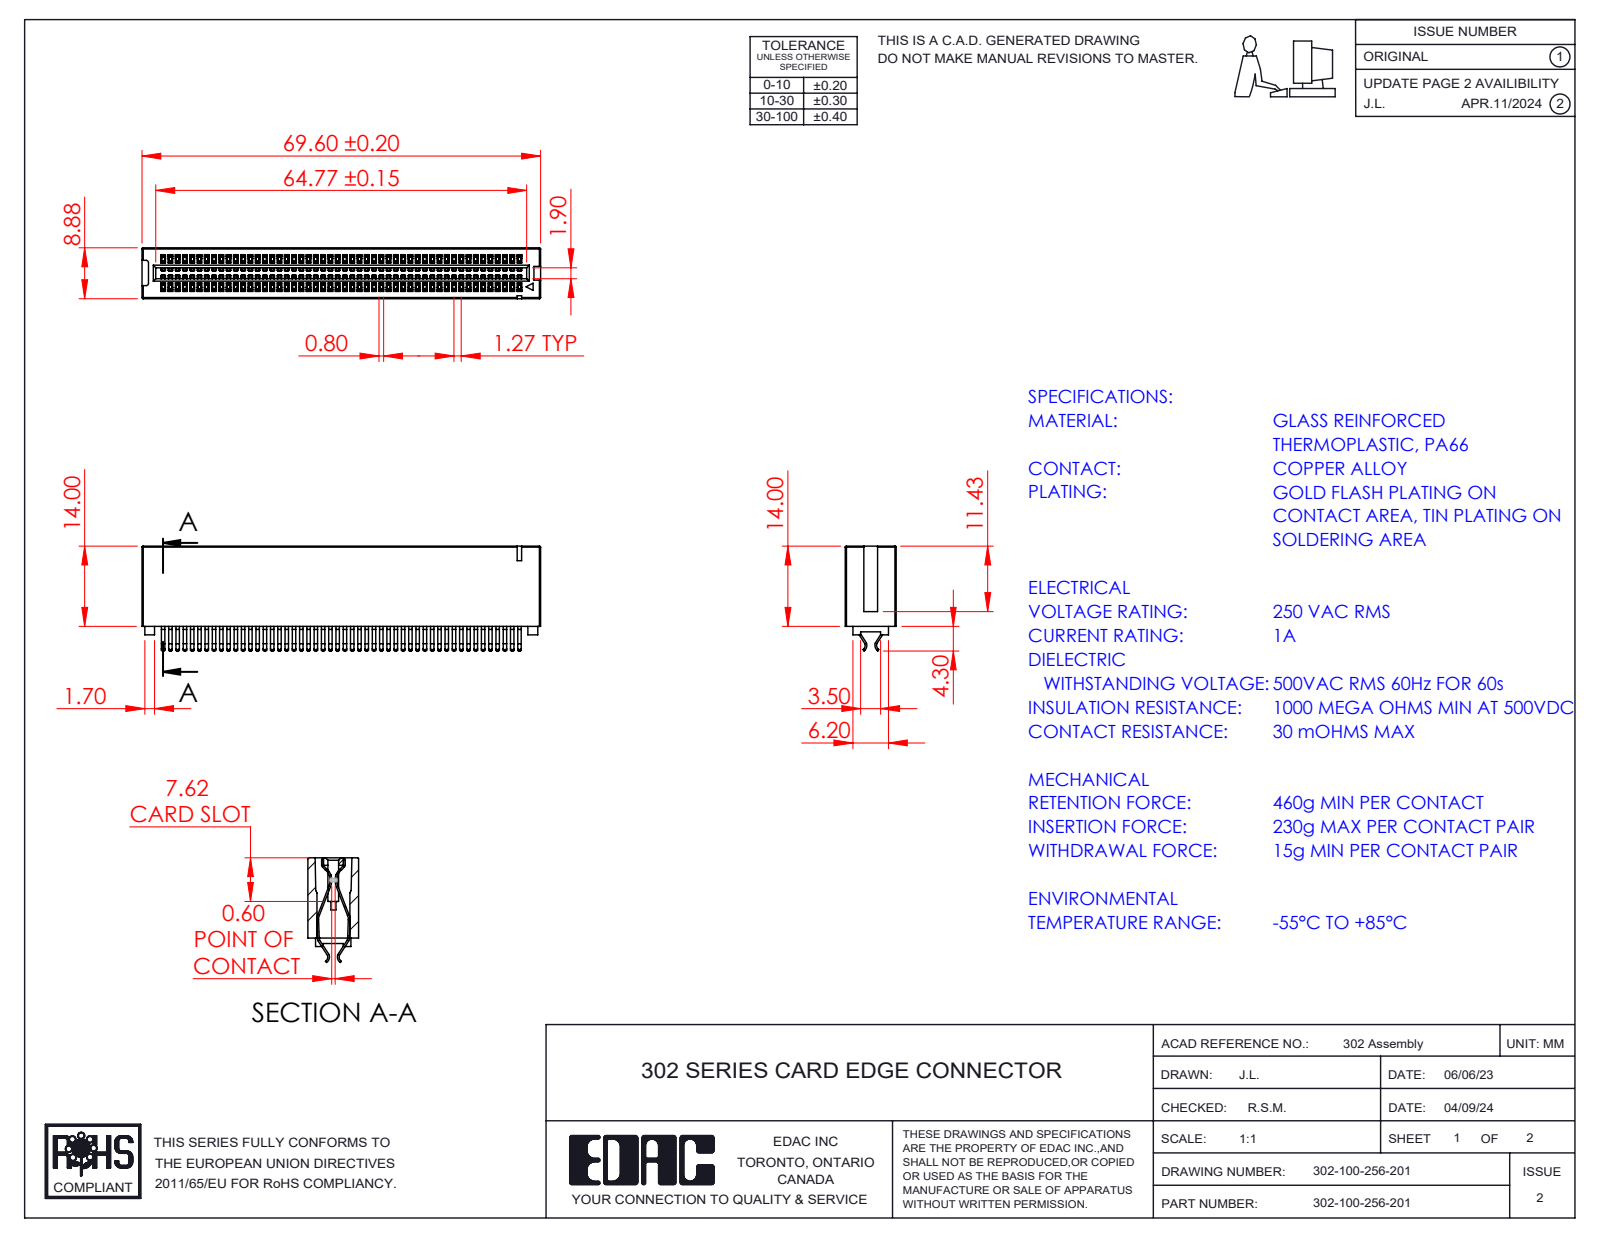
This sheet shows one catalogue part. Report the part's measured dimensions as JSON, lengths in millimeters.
{"part_name": "302-100-256-201; HSG_Vertical HSG; Contact_302-290-X56", "step_written_by": "SolidWorks 2023 (CONFIG_CONTROL_DESIGN)", "units": "millimeters", "bodies": {"solids": 101, "faces": 4816, "planar": 3199, "cylindrical": 1613, "other": 4}, "overall_size": [69.6, 18.3, 8.88], "volume_mm3": 5341, "surface_area_mm2": 15223, "partial_cylinders_radius": [[0.2, 308], [0.11, 2], [0.4, 2], [0.41, 2], [0.93, 2], [1.05, 2], [1.23, 2], [1.25, 2]], "face_to_face_distances": [8.88, 1.27, 0.8, 2.54, 3.8, 0.47, 1.9, 3.49, 5.39, 3.81]}
